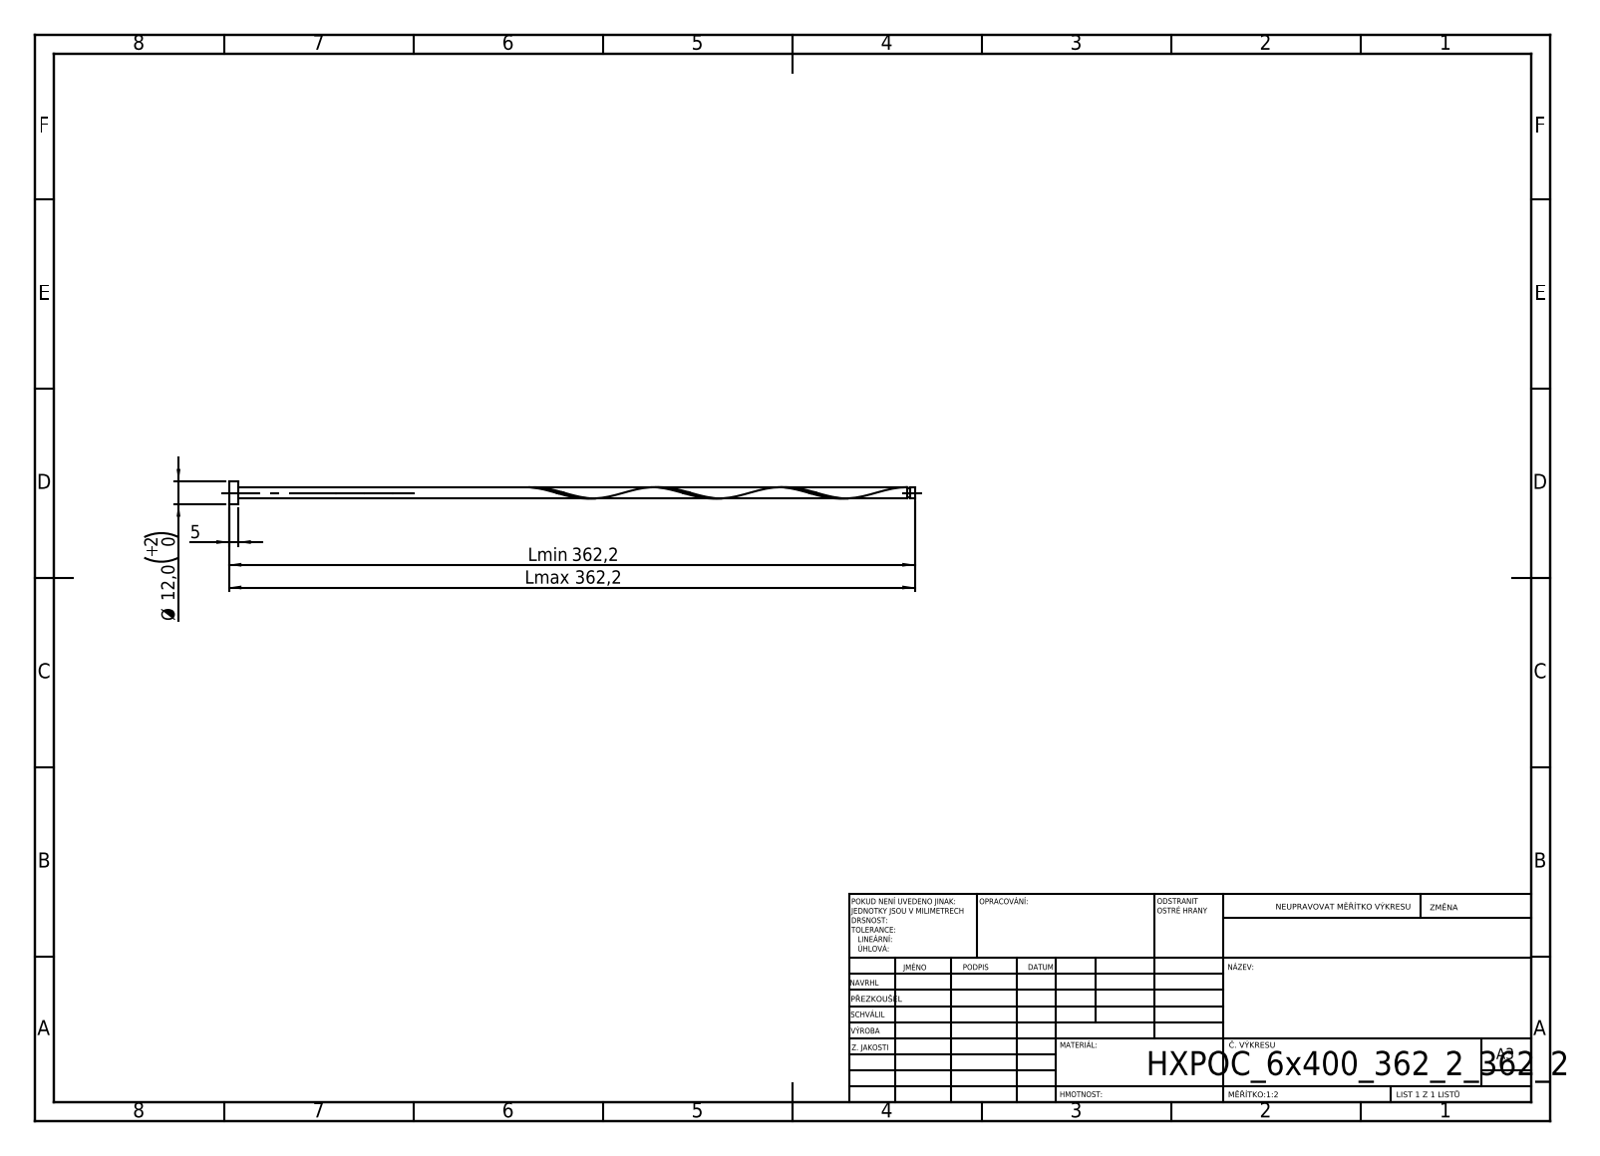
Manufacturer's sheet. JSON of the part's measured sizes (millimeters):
{"step_written_by": "SolidWorks 2019 (CONFIG_CONTROL_DESIGN)", "units": "millimeters", "bodies": {"solids": 1, "faces": 16, "planar": 6, "cylindrical": 9, "other": 1}, "overall_size": [362.2, 12, 12], "volume_mm3": 13059, "surface_area_mm2": 9797, "round_bosses_or_shafts": [[12, 1], [6, 1], [4.8, 1]], "face_to_face_distances": [5, 362.2, 357.2, 359.51, 354.51, 2.69, 358.31, 353.31, 1.2, 3.89]}
